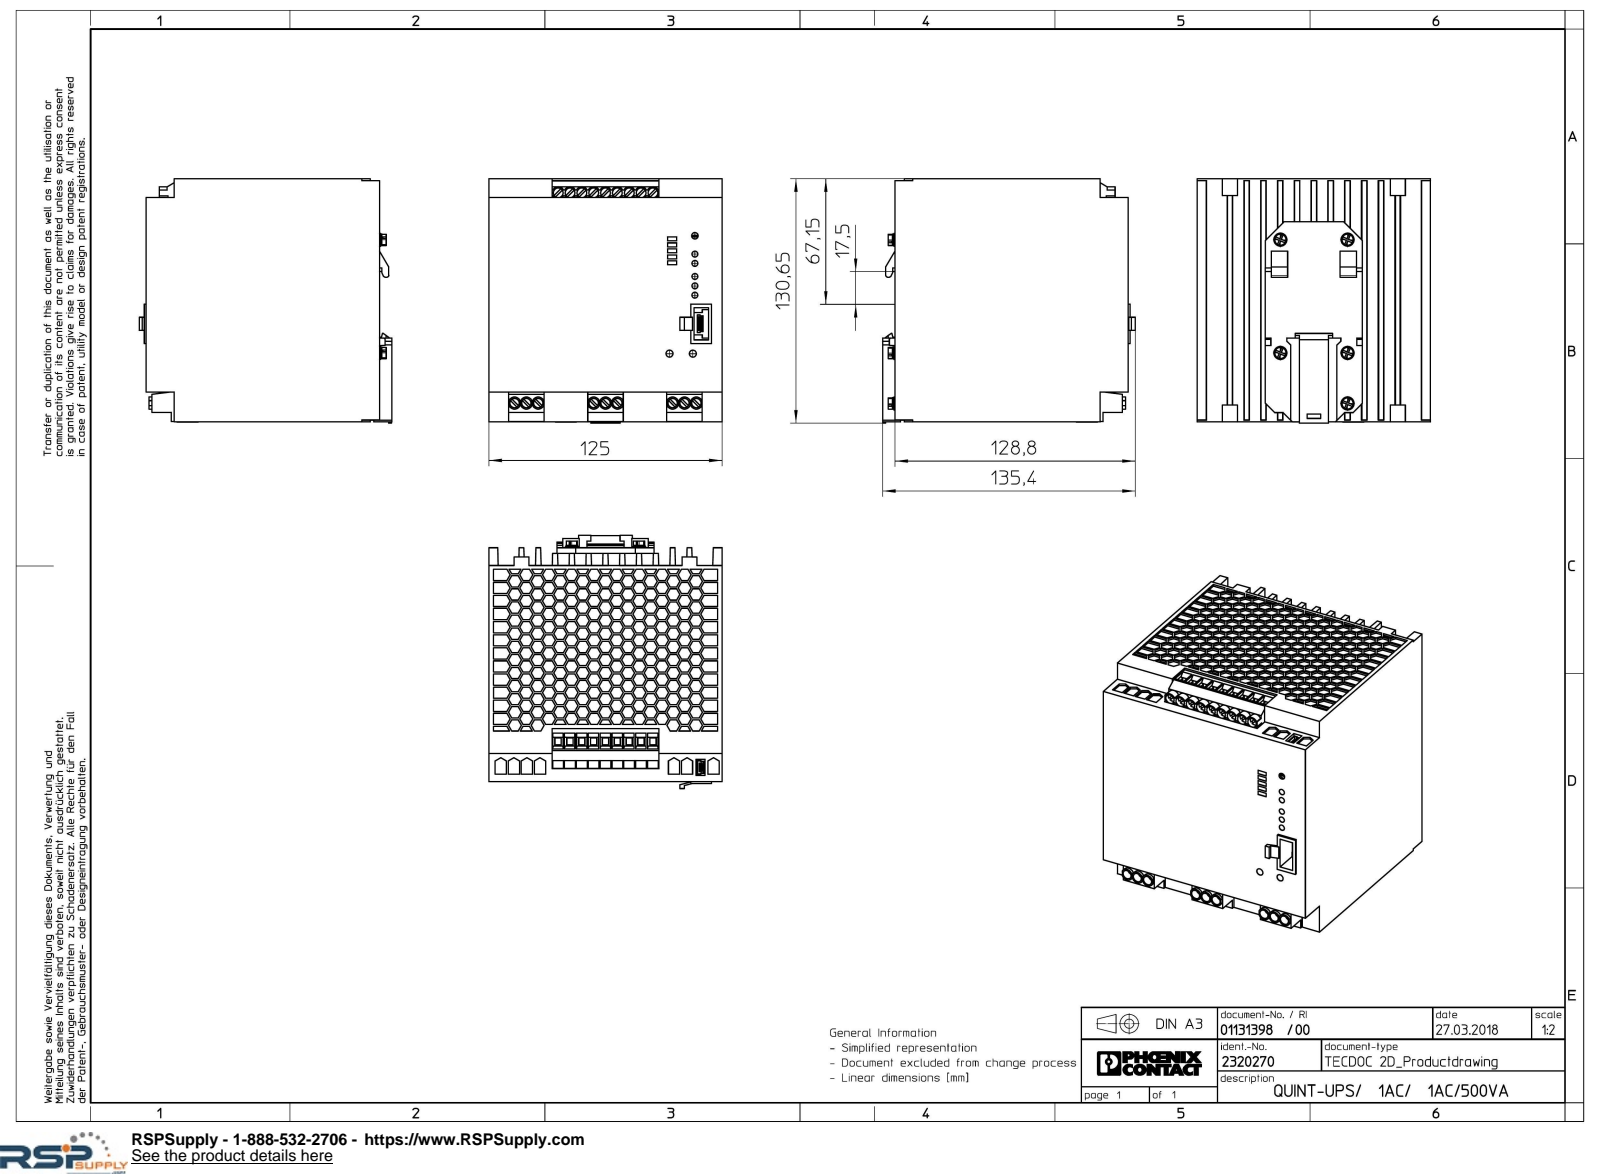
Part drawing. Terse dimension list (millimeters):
name: QUINT_UPS_1AC_1AC_500VA-select
written by: Creo Elements/Direct Modeling 20.1A 29-Sep-2018 (C) Parametric Technology GmbH (AUTOMOTIVE_DESIGN)
unit: mm
bodies: 1 solid, 4500 faces (4374 planar, 126 cylindrical, 0 other)
size: 135.38 × 130.65 × 125
volume: 1 877 000 mm³; area: 149 657 mm²
holes: 9× ⌀5, 9× ⌀5.2, 5× ⌀3.2, 2× ⌀3.8, 1× ⌀3.5, 1× ⌀10
bosses: 5× ⌀7, 5× ⌀6.2, 5× ⌀6, 1× ⌀11.25
rounds: 18× R3.25, 2× R1
face distances: 125, 9, 18, 27, 36, 115.5, 1, 45, 129, 54
hole spacings: 6.35, 12.7, 19.05, 25.4, 31.75, 5, 38.1, 42.29
